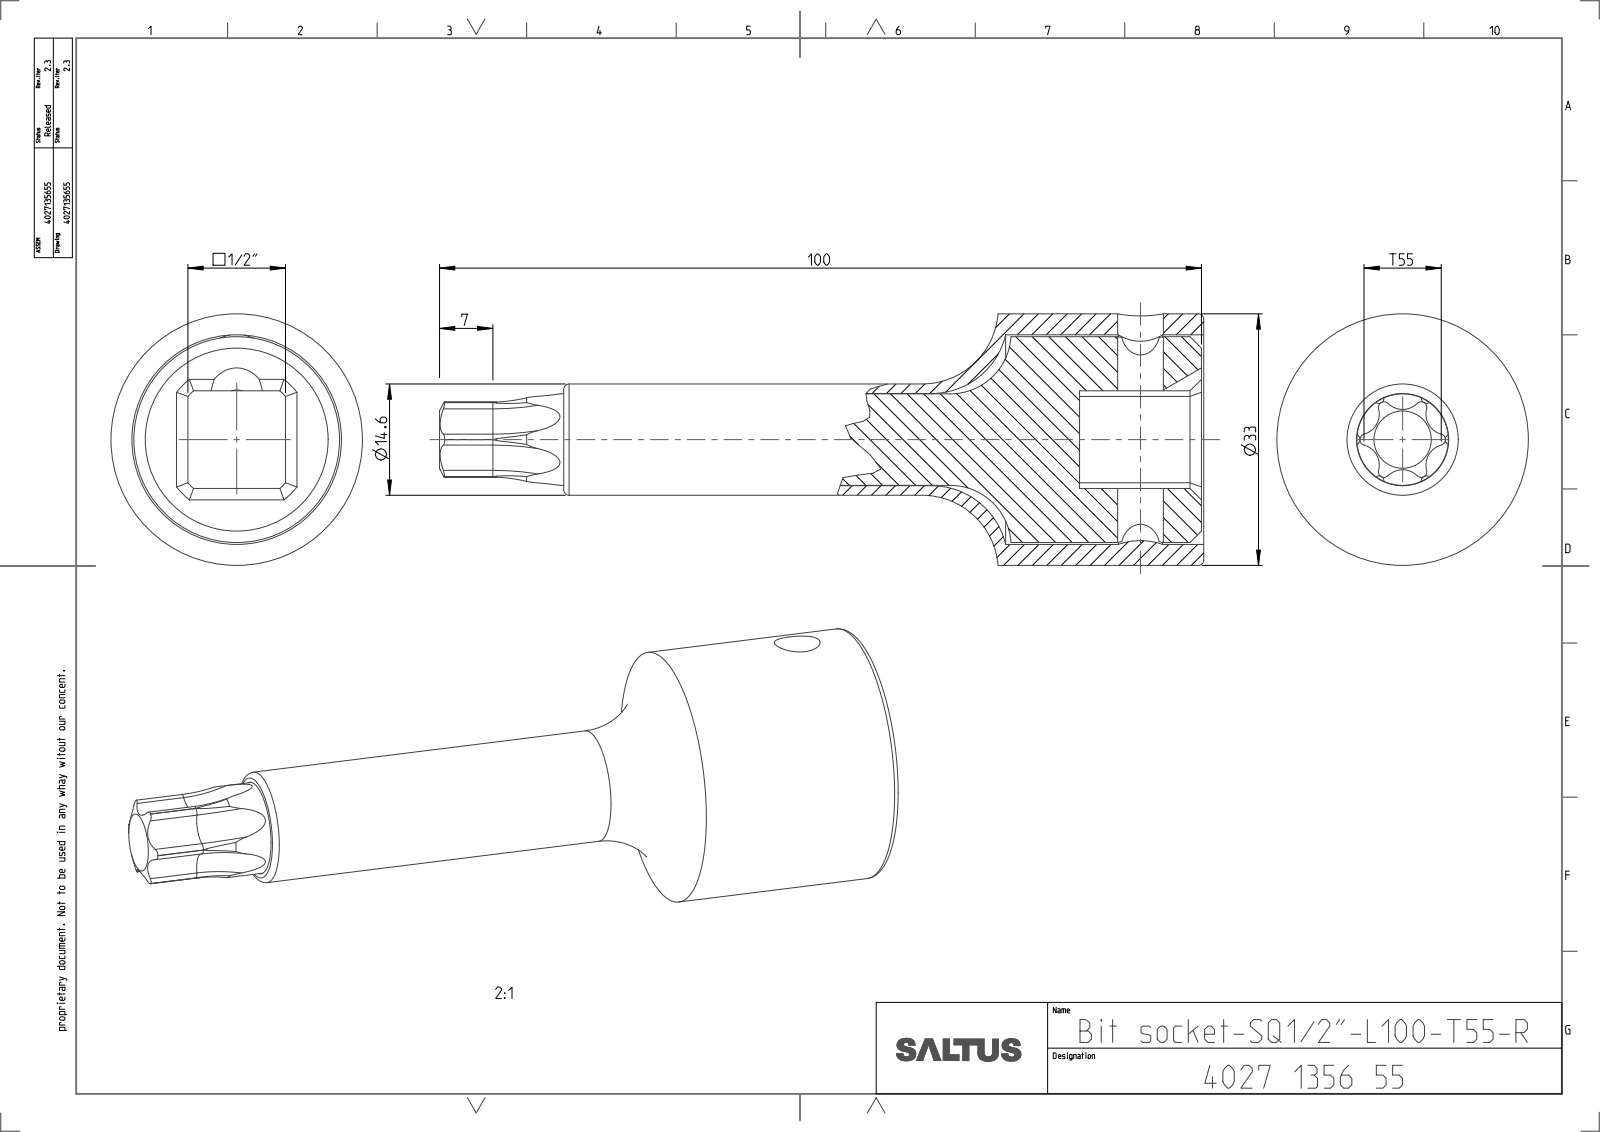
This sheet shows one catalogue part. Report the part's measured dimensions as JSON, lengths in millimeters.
{"part_name": "4027132755; 4027299340; 4027135655_ASM", "step_written_by": "CREO PARAMETRIC BY PTC INC, 2022414 (CONFIG_CONTROL_DESIGN)", "units": "millimeters", "bodies": {"solids": 2, "faces": 110, "planar": 14, "cylindrical": 51, "other": 45}, "overall_size": [100.3, 33, 33], "volume_mm3": 30088, "surface_area_mm2": 17861, "round_holes": [[6, 1], [12.1, 1], [27.5, 1]], "round_bosses_or_shafts": [[33, 1], [27, 1], [14.6, 1], [12, 1]], "partial_cylinders_radius": [[0.73, 12], [2.71, 6], [4, 1], [5.61, 1], [8.55, 1]], "face_to_face_distances": [12.82, 16.3, 16, 84, 100.3, 100, 83.7, 67.7]}
